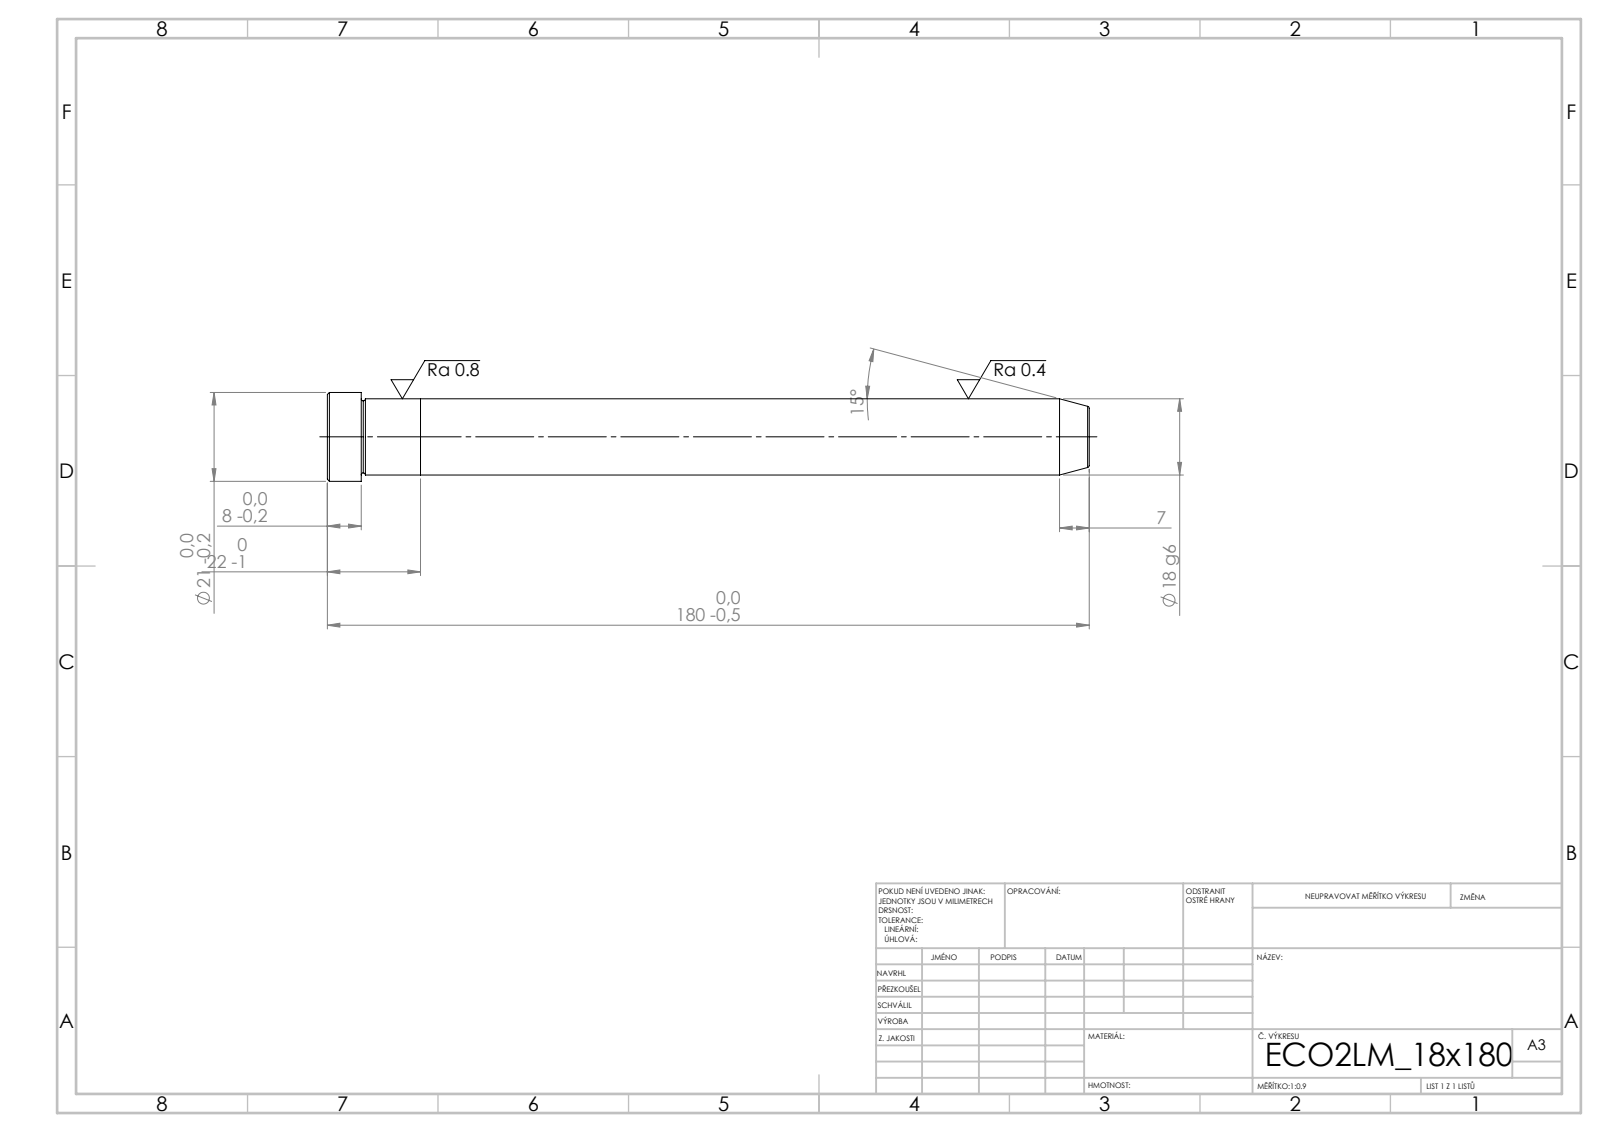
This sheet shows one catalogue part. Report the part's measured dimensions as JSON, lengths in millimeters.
{"step_written_by": "SolidWorks 2019 (CONFIG_CONTROL_DESIGN)", "units": "millimeters", "bodies": {"solids": 2, "faces": 21, "planar": 5, "cylindrical": 6, "other": 10}, "overall_size": [180, 21, 21], "volume_mm3": 46163, "surface_area_mm2": 11336, "round_bosses_or_shafts": [[21, 1], [18, 1]], "face_to_face_distances": [22, 158, 180, 172, 14, 8]}
